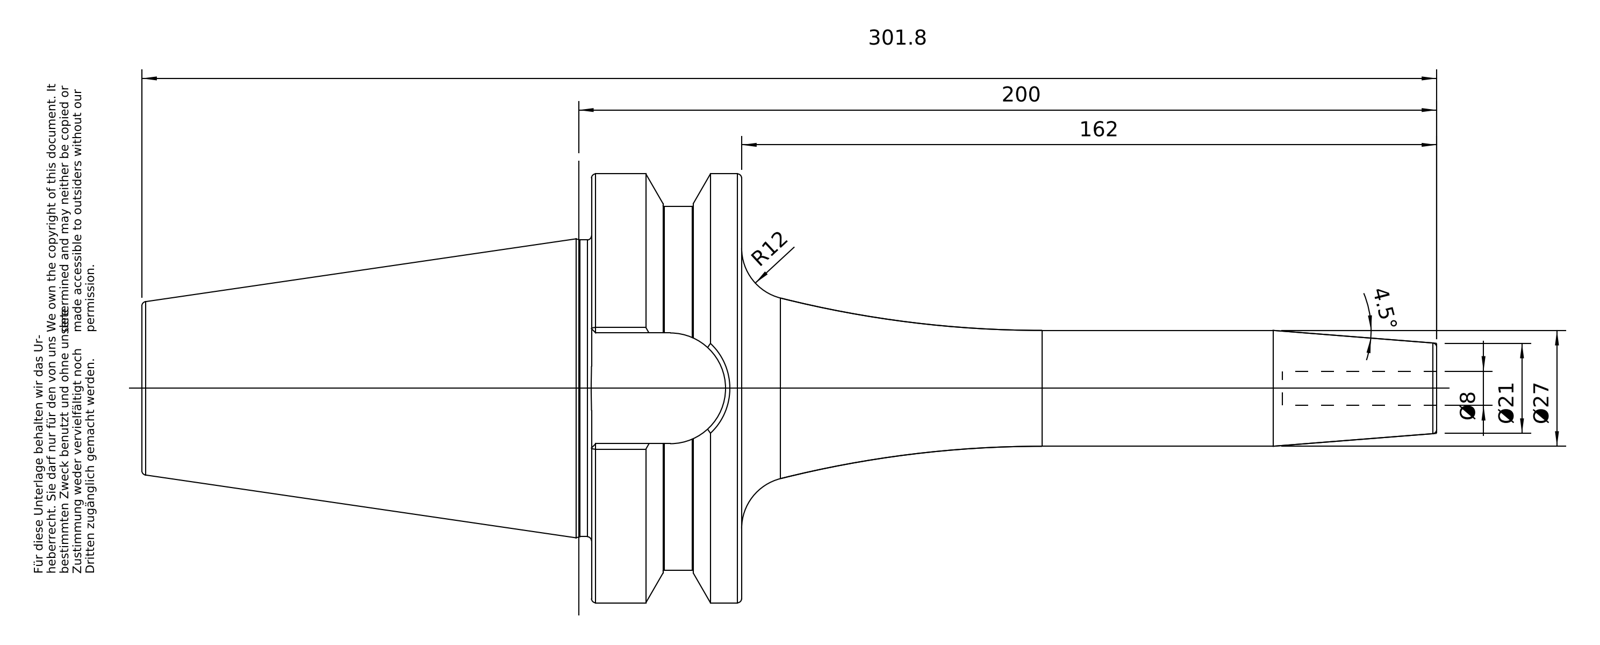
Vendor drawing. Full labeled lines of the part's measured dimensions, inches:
Part name (STEP PRODUCT): 50-646-08
STEP written by: PRO/ENGINEER BY PARAMETRIC TECHNOLOGY CORPORATION, 2010430 (CONFIG_CONTROL_DESIGN)
Units: inches
Bodies: 1 solid, 98 faces (26 planar, 22 cylindrical, 50 other)
Overall size (bounding box): 11.882 × 3.936 × 3.936
Volume: 35.46 in³ · Surface area: 102.2 in²
Round holes (diameter × count): ⌀0.315 ×1, ⌀0.817 ×1, ⌀0.985 ×1, ⌀1.012 ×1
Round bosses / shafts (diameter × count): ⌀3.936 ×1, ⌀3.337 ×1, ⌀2.722 ×1, ⌀1.063 ×1, ⌀0.945 ×1
Partial cylindrical surfaces — rounded edges, fillets, slot ends (radius × count): R0.508 ×1
Main face-to-face distances: 1.378, 2.772, 4.126, 5.504, 1.016, 11.882, 7.756, 6.378, 1.89, 2.236
